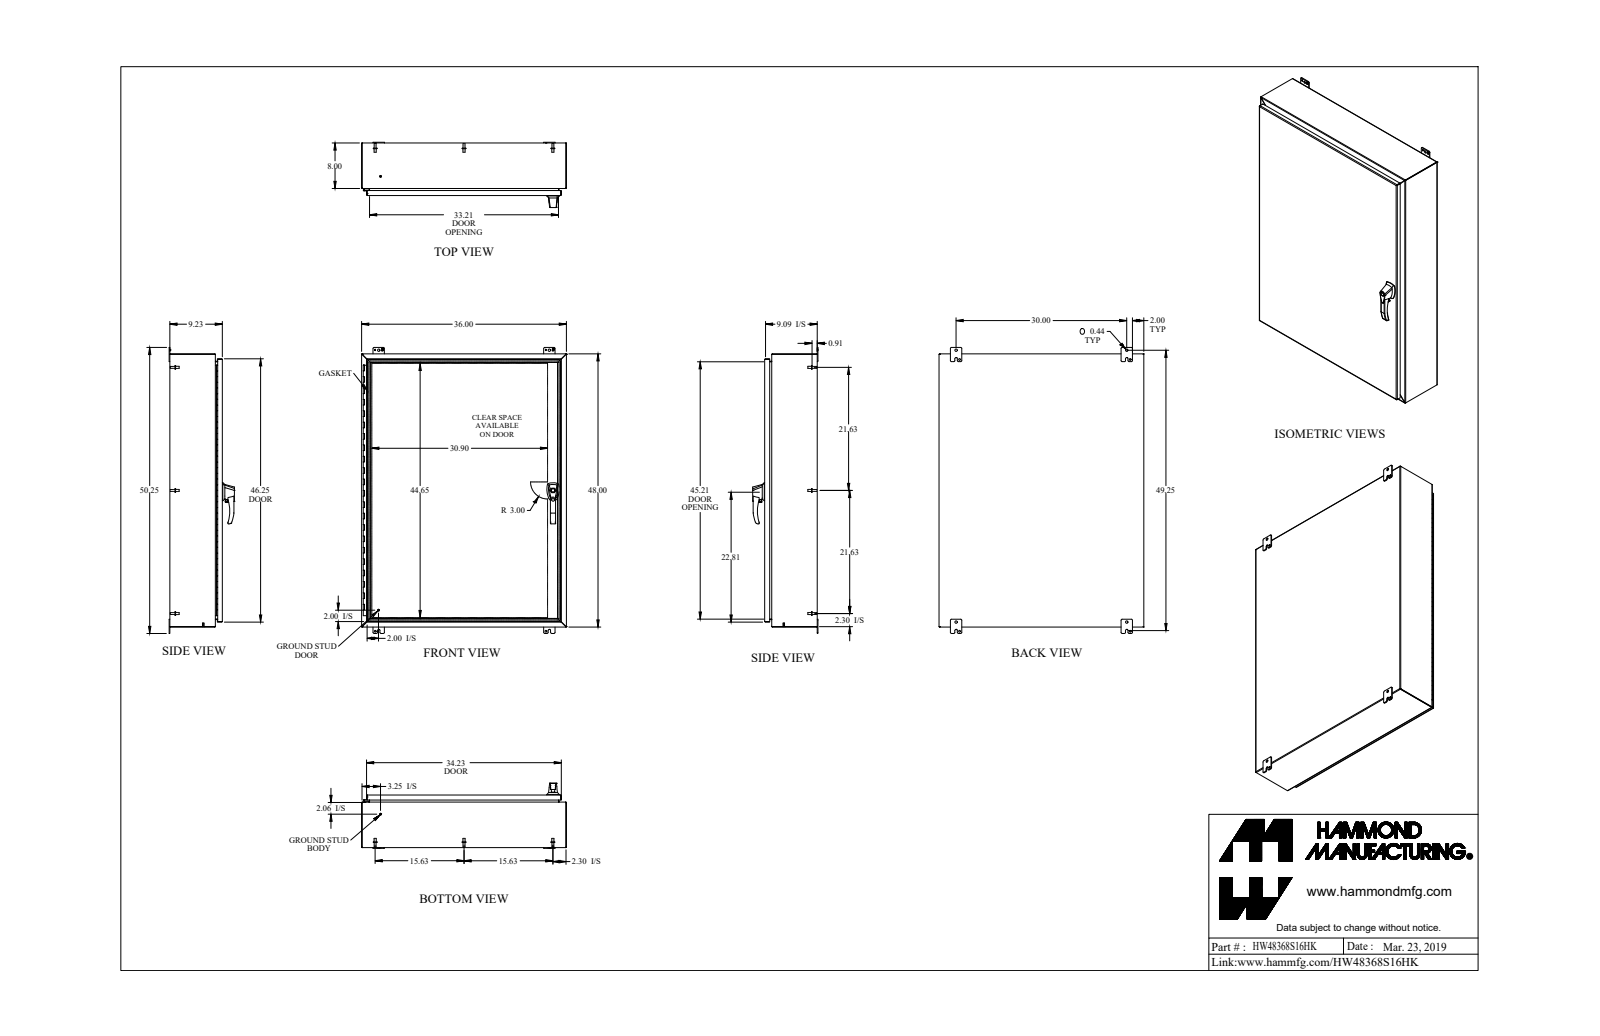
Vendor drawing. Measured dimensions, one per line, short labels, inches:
name: HW48368S16HK
written by: SolidWorks 2018 (AUTOMOTIVE_DESIGN)
unit: in
bodies: 45 solids, 1676 faces (768 planar, 732 cylindrical, 176 other)
size: 50.25 × 36 × 11.473
volume: 458.9 in³; area: 11 213 in²
holes: 6× ⌀0.176, 4× ⌀0.313, 3× ⌀0.25, 3× ⌀0.265, 3× ⌀0.413, 2× ⌀0.196, 2× ⌀0.256, 2× ⌀0.394, 2× ⌀0.437, 1× ⌀0.11, 1× ⌀0.233, 1× ⌀0.33
bosses: 13× ⌀0.375, 8× ⌀0.65, 8× ⌀0.332, 7× ⌀0.25, 6× ⌀0.156, 3× ⌀1, 2× ⌀0.63, 2× ⌀0.51
rounds: 27× R0.25, 20× R0.188, 16× R0.036, 16× R0.108, 12× R0.06, 9× R0.125, 8× R0.045, 8× R0.218
face distances: 0.072, 9.138, 9.066, 0.095, 9.233, 9.161, 35.928, 47.928, 7.928, 35.856
hole spacings: 20.118, 20.119, 40.237, 1.11, 1.111, 20.119, 20.887, 30
